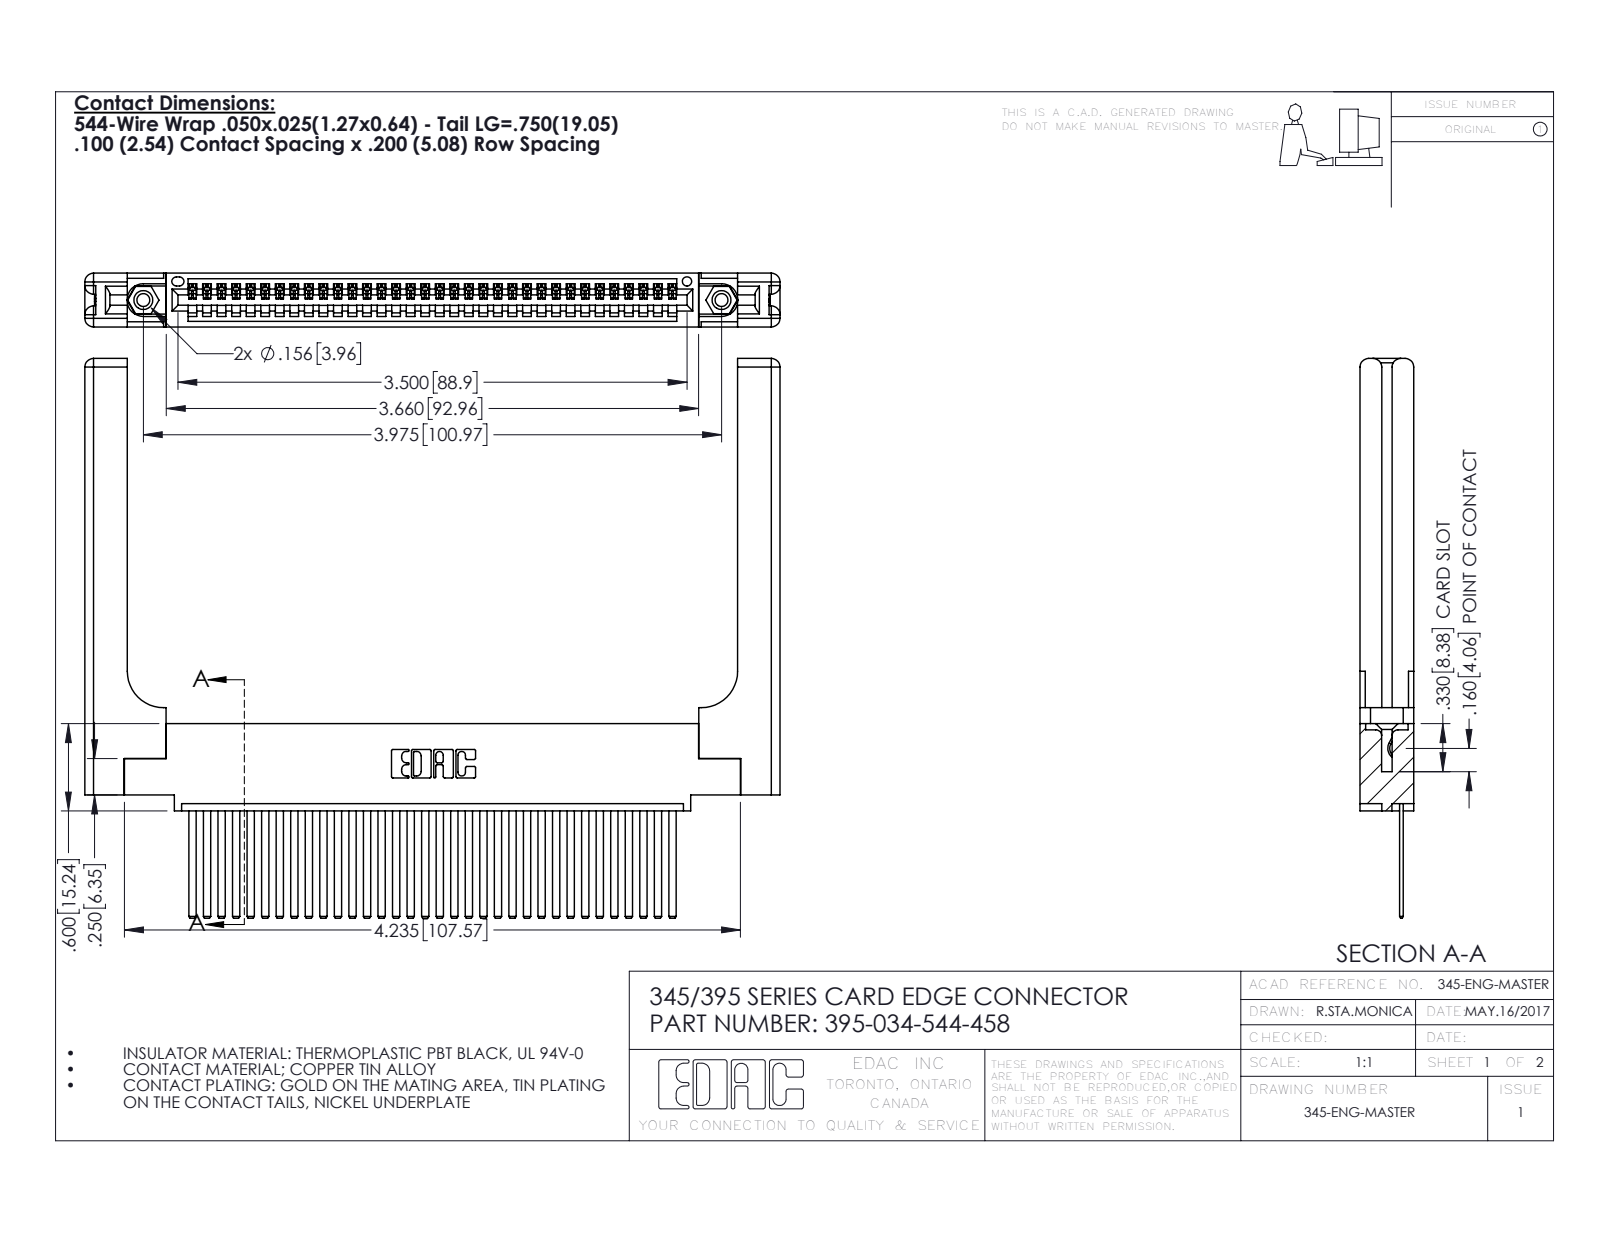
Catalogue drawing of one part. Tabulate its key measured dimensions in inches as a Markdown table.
| quantity | value |
| --- | --- |
| part name | 345-292-001_345-293-144; 345-250-001_345-250-001-102; 345-220-058_345-220-058; 395-034-544-458 (+1 more) |
| STEP written by | SolidWorks 2016 (CONFIG_CONTROL_DESIGN) |
| units | inches |
| bodies | 39 solids, 2154 faces (1456 planar, 638 cylindrical, 60 other) |
| overall size | 4.779 × 3.847 × 0.37 |
| volume | 1.238 in³ |
| surface area | 34.29 in² |
| round holes (diameter × count) | 0.089 × 2, 0.125 × 2, 0.156 × 2, 0.064 × 1 |
| round bosses / shafts (diameter × count) | 0.155 × 2 |
| partial cylindrical surfaces (radius × count) | 0.006 × 68, 0.01 × 22, 0.06 × 16, 0.007 × 6, 0.031 × 6, 0.026 × 3, 0.03 × 2, 0.031 × 2 |
| main face-to-face distances | 0.072, 0.298, 0.37, 0.098, 0.272, 0.025, 0.2, 0.148, 0.15, 0.077 |
| hole center spacings | 0.27, 3.74, 3.975 |
